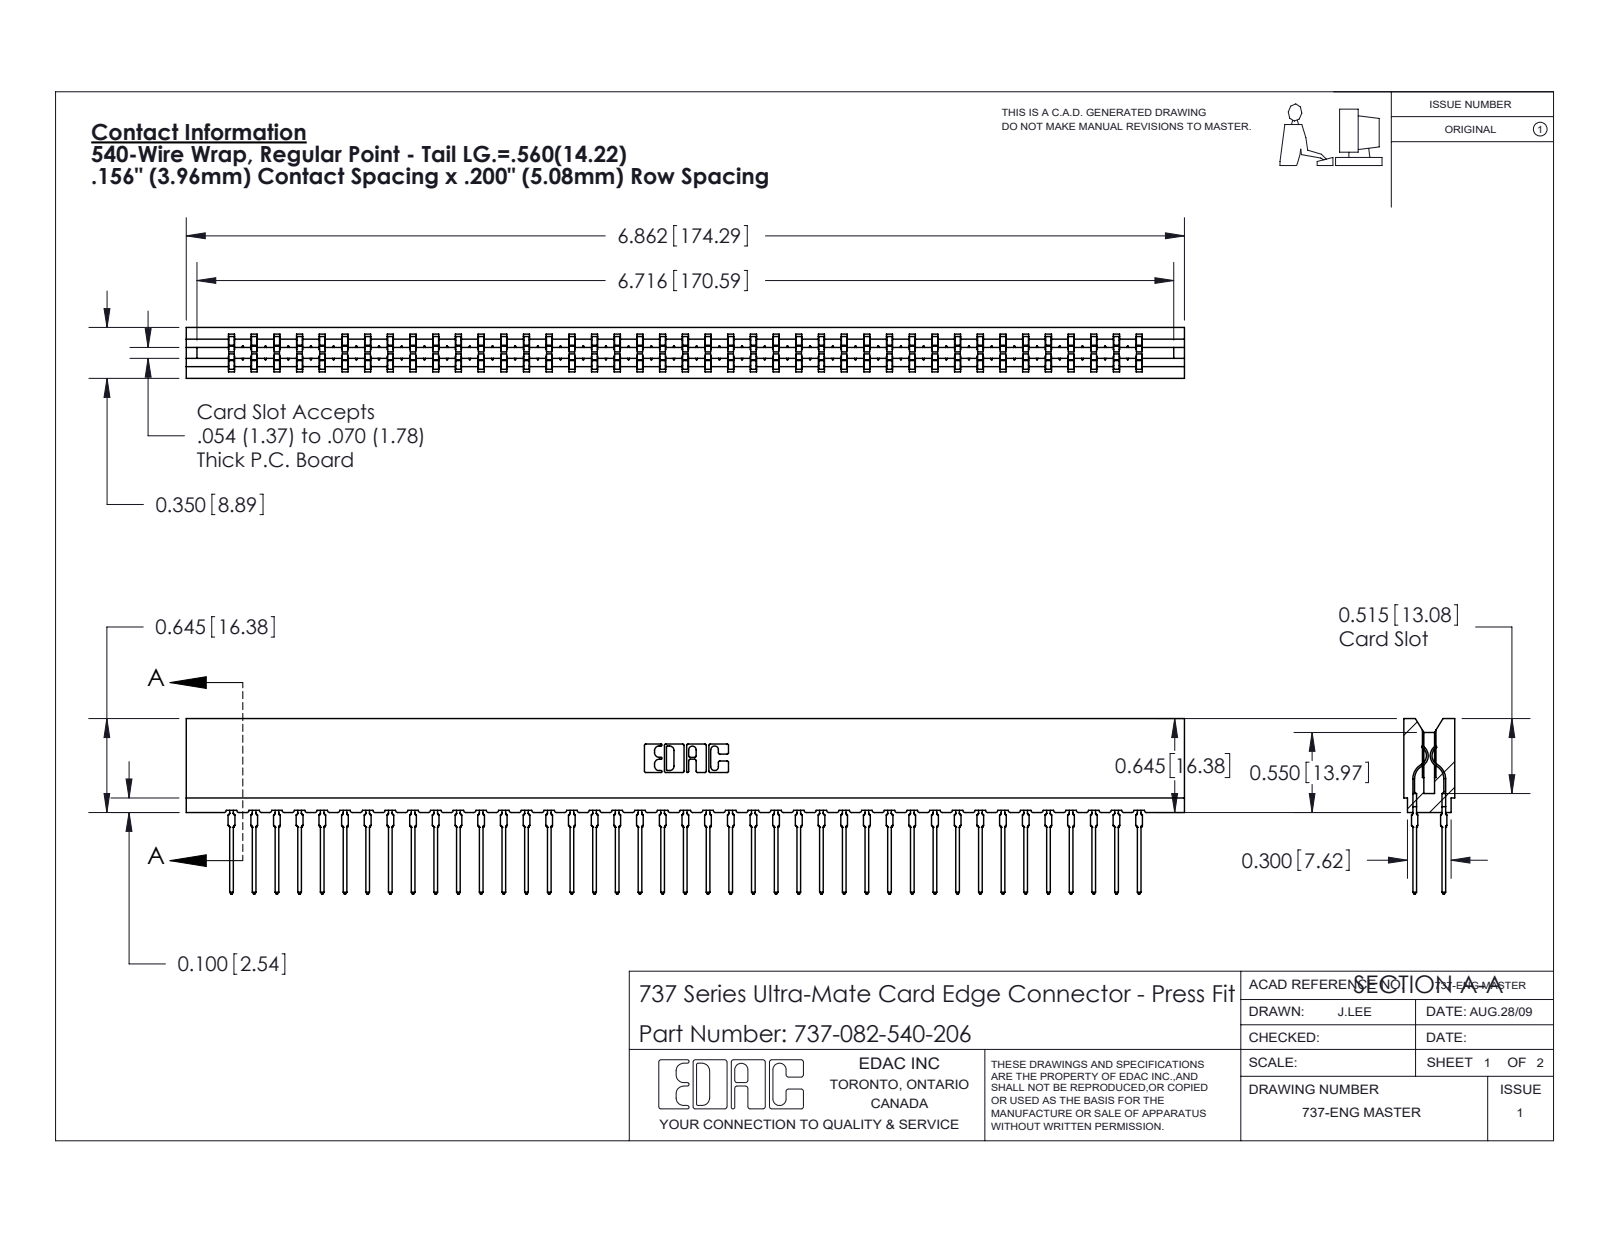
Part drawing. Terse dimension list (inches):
name: 745-292-001_540; 737 Part_Insulator Option - 06; 737-082-540-206
written by: SolidWorks 2020 (CONFIG_CONTROL_DESIGN)
unit: in
bodies: 83 solids, 7475 faces (3868 planar, 1475 cylindrical, 2132 other)
size: 6.862 × 1.206 × 0.35
volume: 1.065 in³; area: 40.97 in²
rounds: 164× R0.021, 82× R0.015, 22× R0.01, 8× R0.005, 8× R0.011, 6× R0.007, 6× R0.031, 3× R0.026
face distances: 0.138, 0.212, 0.35, 0.063, 0.287, 0.076, 0.149, 0.074, 0.045, 0.305
